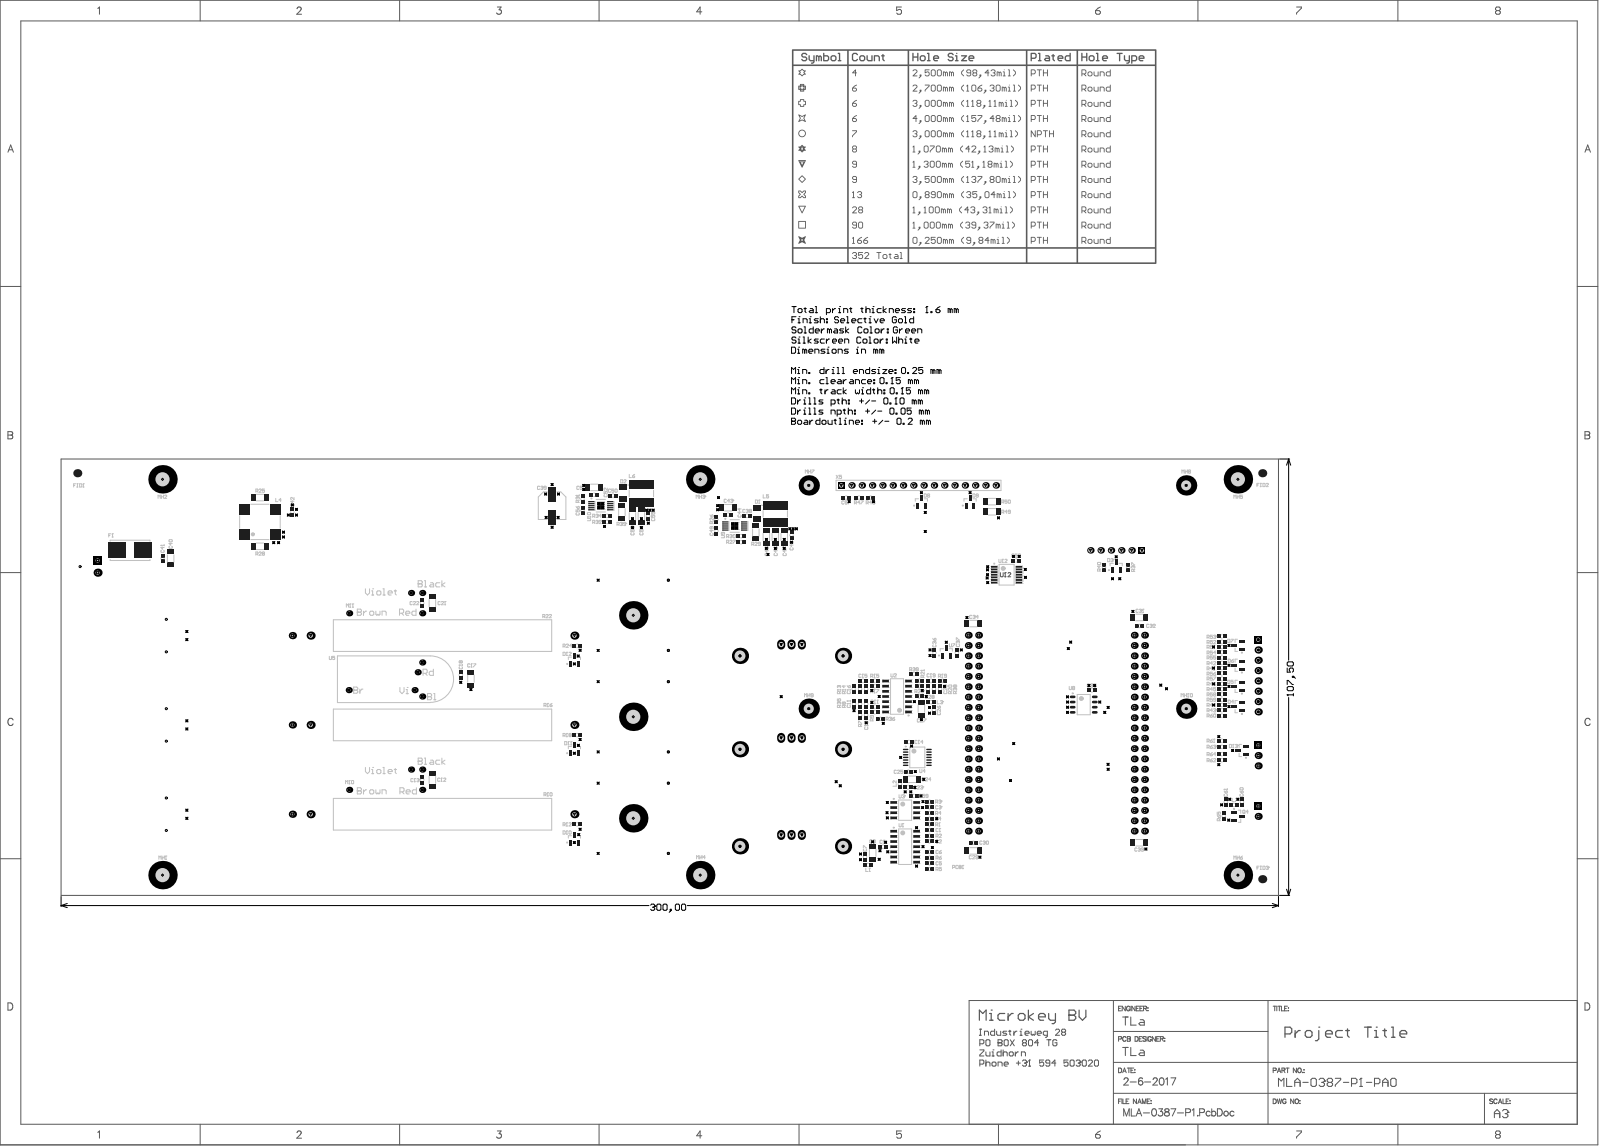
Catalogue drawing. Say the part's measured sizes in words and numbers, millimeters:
The part is named "PCB; Board; MP14; 9774080151 (+6 more)". Its 3-D file was written by "Open CASCADE 6.8 (AUTOMOTIVE_DESIGN)". It is 574 solids with 10280 faces: 7849 planar, 1726 cylindrical and 705 other. Overall it measures 300 by 107.5 by 53.19 millimeters. Its volume is 138 173 cubic millimeters and its surface area 131 676 square millimeters. Round holes: 87 of diameter 1, 36 of diameter 1.1, 15 of diameter 0.89, 11 of diameter 3, 10 of diameter 1.07, 8 of diameter 1.7, 6 of diameter 2.3, 6 of diameter 2.46, 6 of diameter 2.7, 6 of diameter 4, 6 of diameter 4.4, 4 of diameter 1.57. Round bosses or shafts: 14 of diameter 1.8, 6 of diameter 6, 6 of diameter 4.2, 6 of diameter 0.85, 4 of diameter 5.1, 4 of diameter 4.35, 4 of diameter 3.5, 4 of diameter 2.8. Partial cylindrical surfaces (rounded edges, fillets, slot ends): 178 of radius 0.1, 117 of radius 0.13, 74 of radius 0.2, 18 of radius 0.3, 12 of radius 0.3, 12 of radius 0.75, 11 of radius 0.5, 8 of radius 0.15. The main face-to-face distances are 1.85, 12.24, 10.39, 1.6, 11.99, 13.84, 1.5, 21.8, 5.75, 22.75. The hole center spacings are 12.23, 23, 17.3, 10.16, 18.5, 67.5, 83.8, 2.5.
